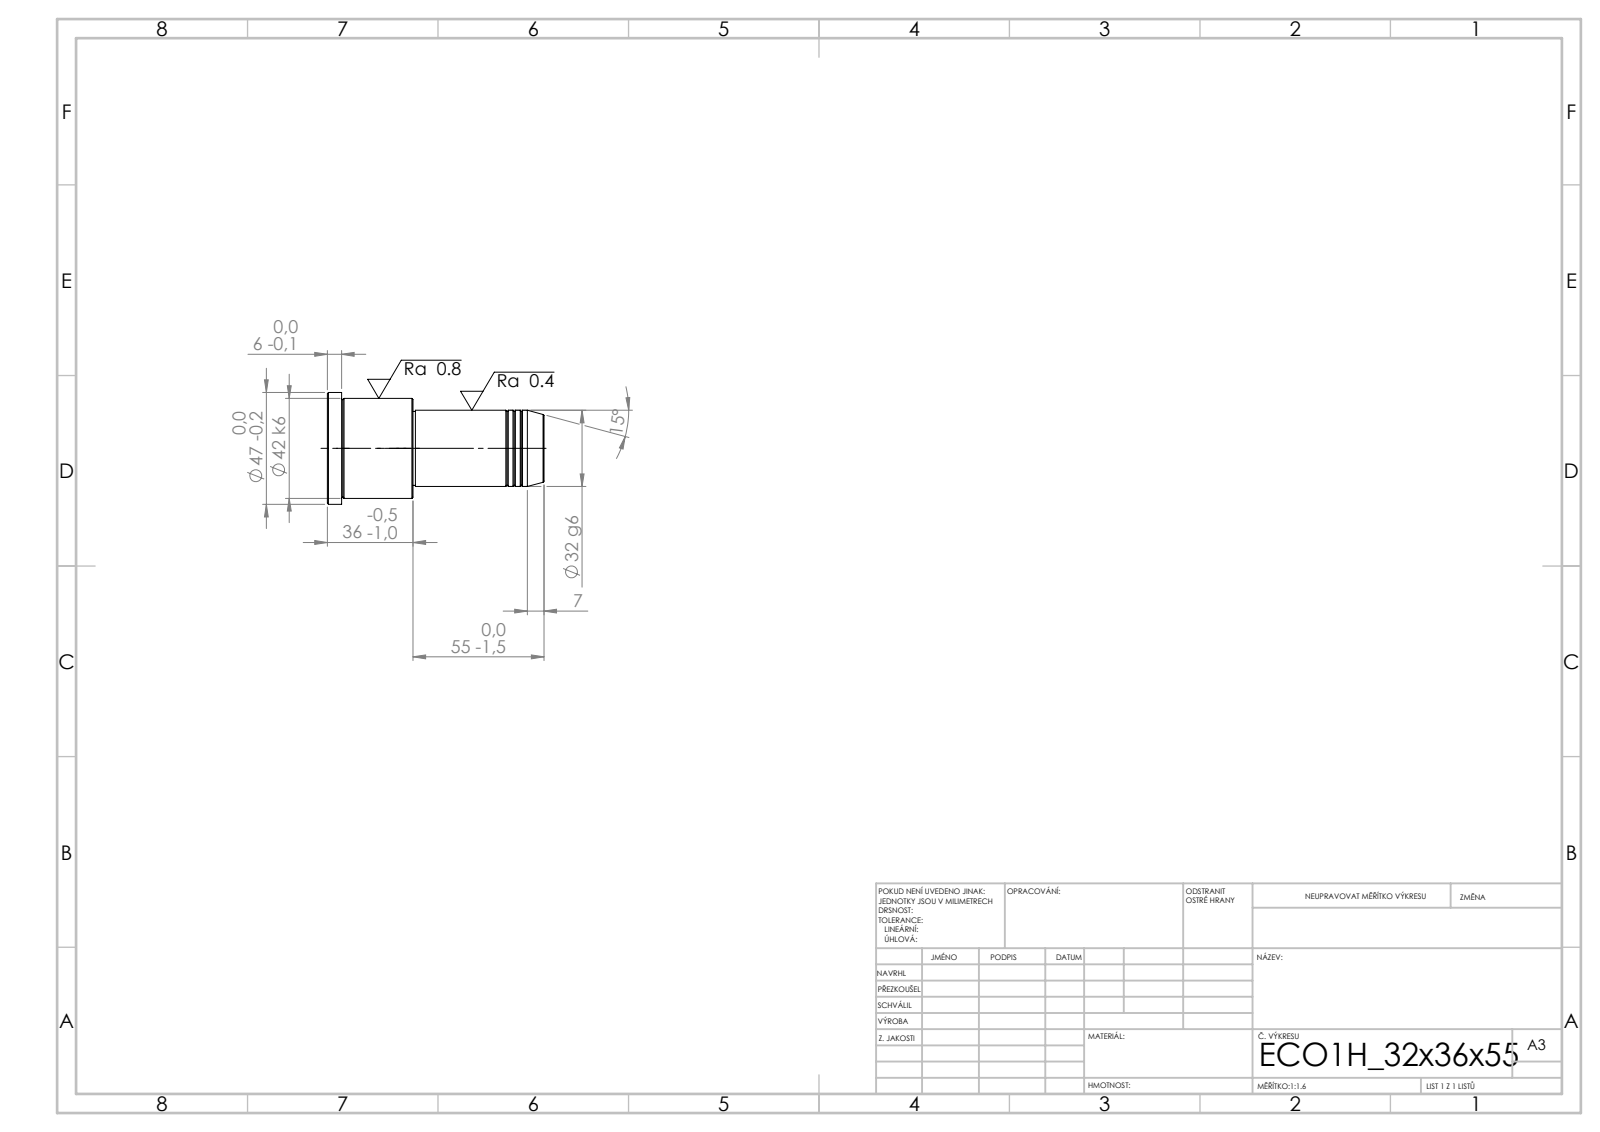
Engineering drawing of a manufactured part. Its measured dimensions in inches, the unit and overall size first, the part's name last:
Units: inches
Overall size (bounding box): 3.583 × 1.85 × 1.85
Round bosses / shafts (diameter × count): ⌀1.85 ×1, ⌀1.654 ×1, ⌀1.26 ×1, ⌀1.22 ×1
Main face-to-face distances: 3.583, 2.165, 1.417, 3.346, 1.181, 0.236, 2.126, 0.039, 1.22, 1.457
Volume: 5.817 in³ · Surface area: 21.52 in²
Bodies: 1 solid, 43 faces (5 planar, 14 cylindrical, 24 other)
STEP written by: SolidWorks 2019 (CONFIG_CONTROL_DESIGN)
